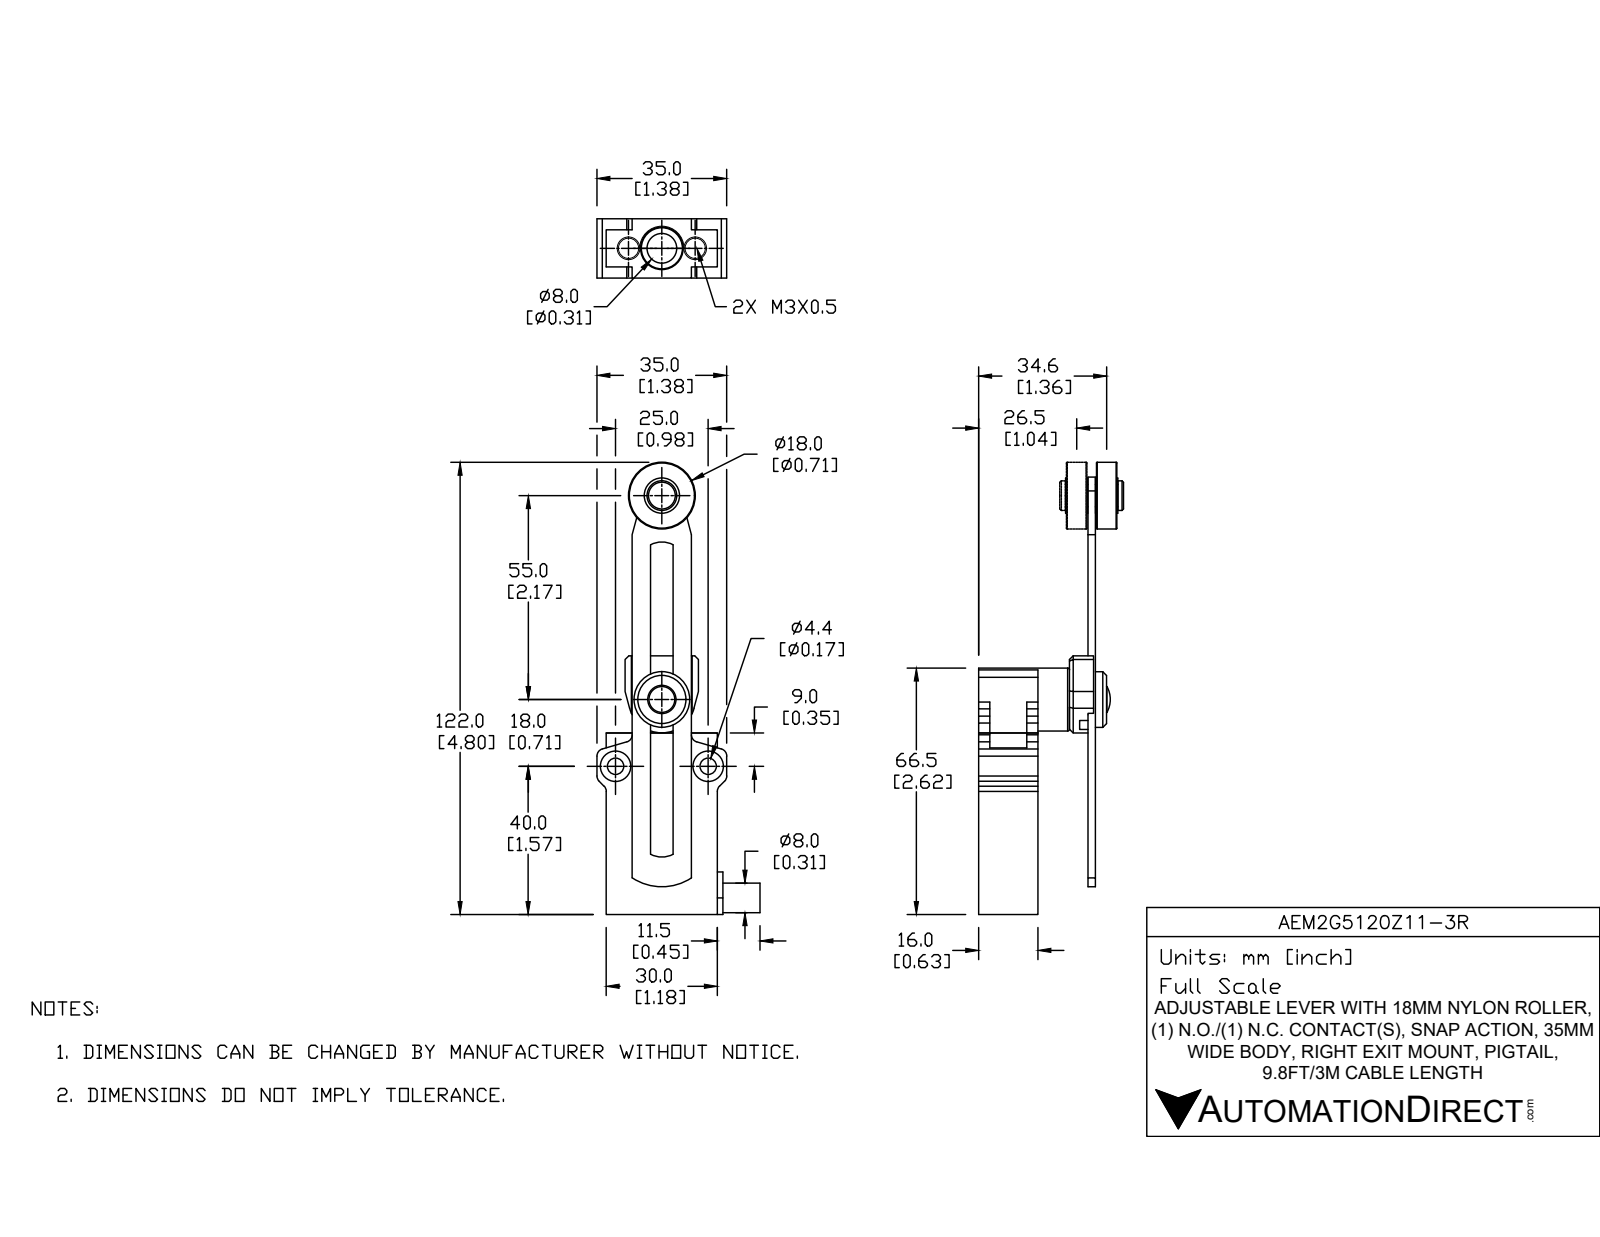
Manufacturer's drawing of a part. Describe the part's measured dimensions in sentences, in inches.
The part is named "AEM2G5120Z11-3R". Its 3-D file was written by "SolidWorks 2017 (AUTOMOTIVE_DESIGN)". It is 9 solids with 437 faces: 194 planar, 179 cylindrical and 64 other. Overall it measures 4.941 by 1.87 by 1.587 inches. Its volume is 2.01 cubic inches and its surface area 24.27 square inches. Round holes: 2 of diameter 0.118, 2 of diameter 0.161, 2 of diameter 0.173, 2 of diameter 0.323, 1 of diameter 0.098, 1 of diameter 0.138, 1 of diameter 0.197, 1 of diameter 0.224, 1 of diameter 0.24, 1 of diameter 0.299. Round bosses or shafts: 1 of diameter 0.709, 1 of diameter 0.622, 1 of diameter 0.591, 1 of diameter 0.394, 1 of diameter 0.323, 1 of diameter 0.276, 1 of diameter 0.236, 1 of diameter 0.157. Partial cylindrical surfaces (rounded edges, fillets, slot ends): 36 of radius 0.006, 10 of radius 0.079, 4 of radius 0.008, 4 of radius 0.047, 3 of radius 0.039, 3 of radius 0.256, 2 of radius 0.031, 1 of radius 0.059. The main face-to-face distances are 0.63, 1.291, 0.661, 0.047, 1.181, 0.614, 1.244, 1.929, 0.28, 0.902. The hole center spacings are 0.863, 0.748, 0.984, 2.304, 3.052, 3.053.
